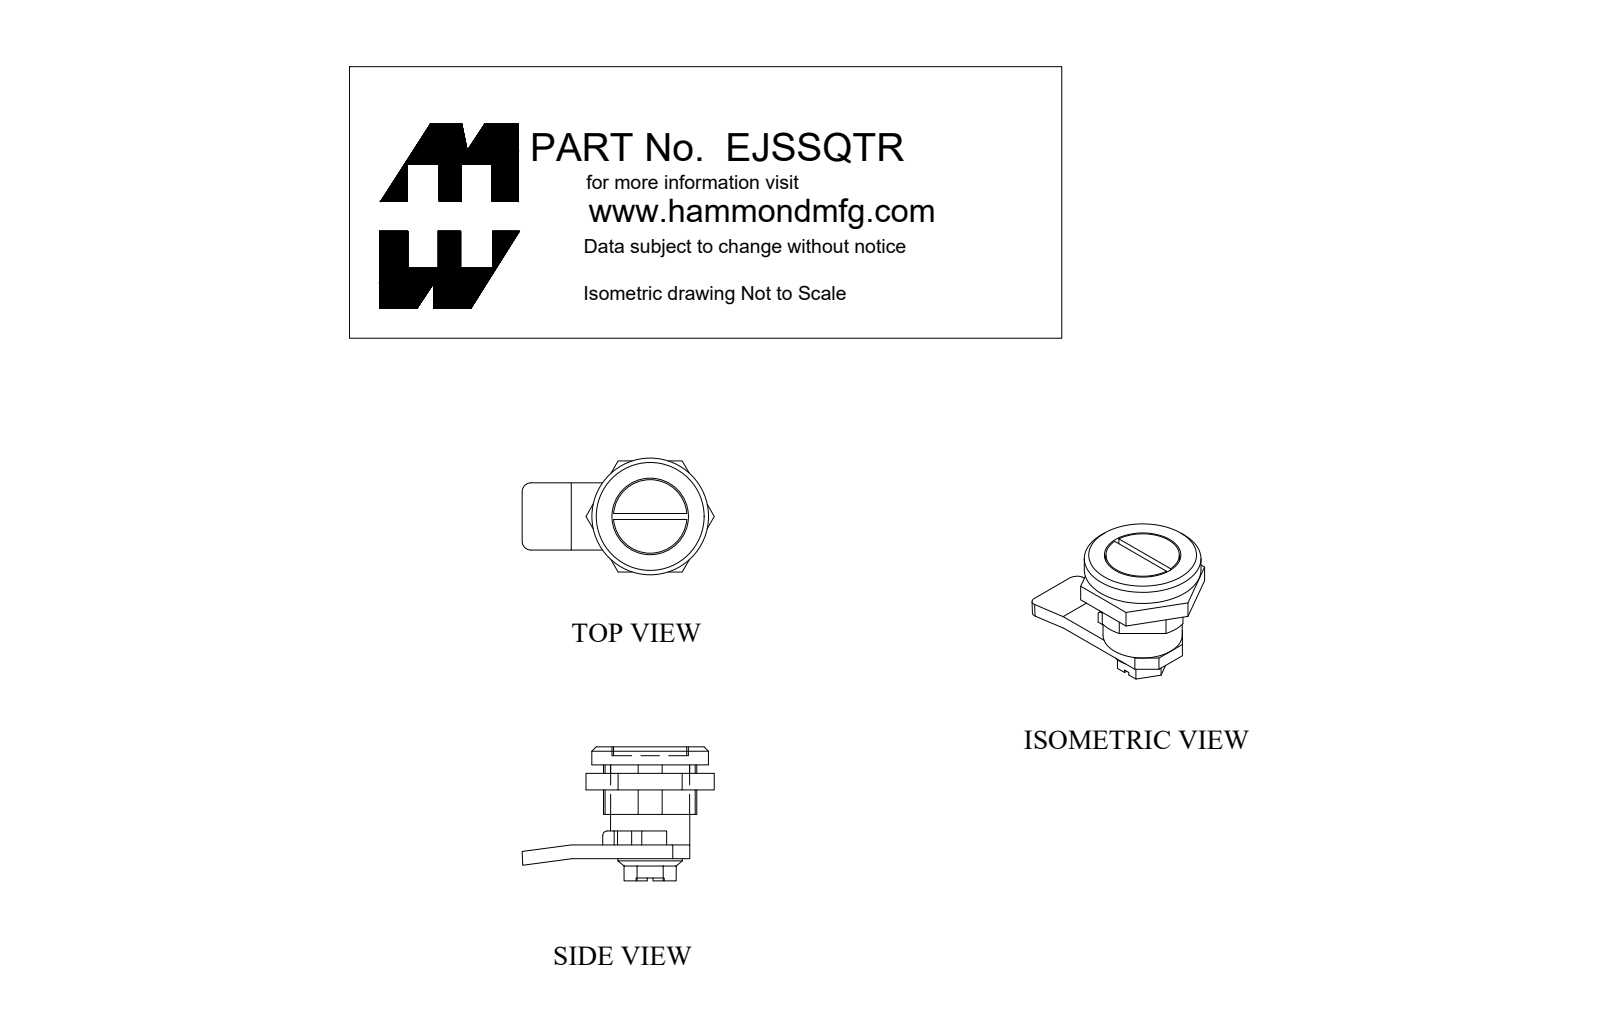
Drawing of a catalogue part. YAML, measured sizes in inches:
part_name: "EJSSQTR_Default"
step_written_by: "SolidWorks 2019 (CONFIG_CONTROL_DESIGN)"
units: inches
bodies: {solids: 1, faces: 100, planar: 71, cylindrical: 25, other: 4}
overall_size: [1.298, 0.905, 0.788]
volume: 0.273
surface_area: 4.179
round_holes:
  - {diameter: 0.516, count: 1}
round_bosses_or_shafts:
  - {diameter: 0.788, count: 1}
  - {diameter: 0.535, count: 1}
  - {diameter: 0.496, count: 1}
  - {diameter: 0.435, count: 1}
partial_cylinders:
  - {radius: 0.06, count: 2}
  - {radius: 0.03, count: 1}
  - {radius: 0.125, count: 1}
  - {radius: 0.315, count: 1}
face_to_face_distances: [0.093, 0.122, 0.057, 0.179, 0.112, 0.169, 0.291, 0.464, 0.576, 0.633]
